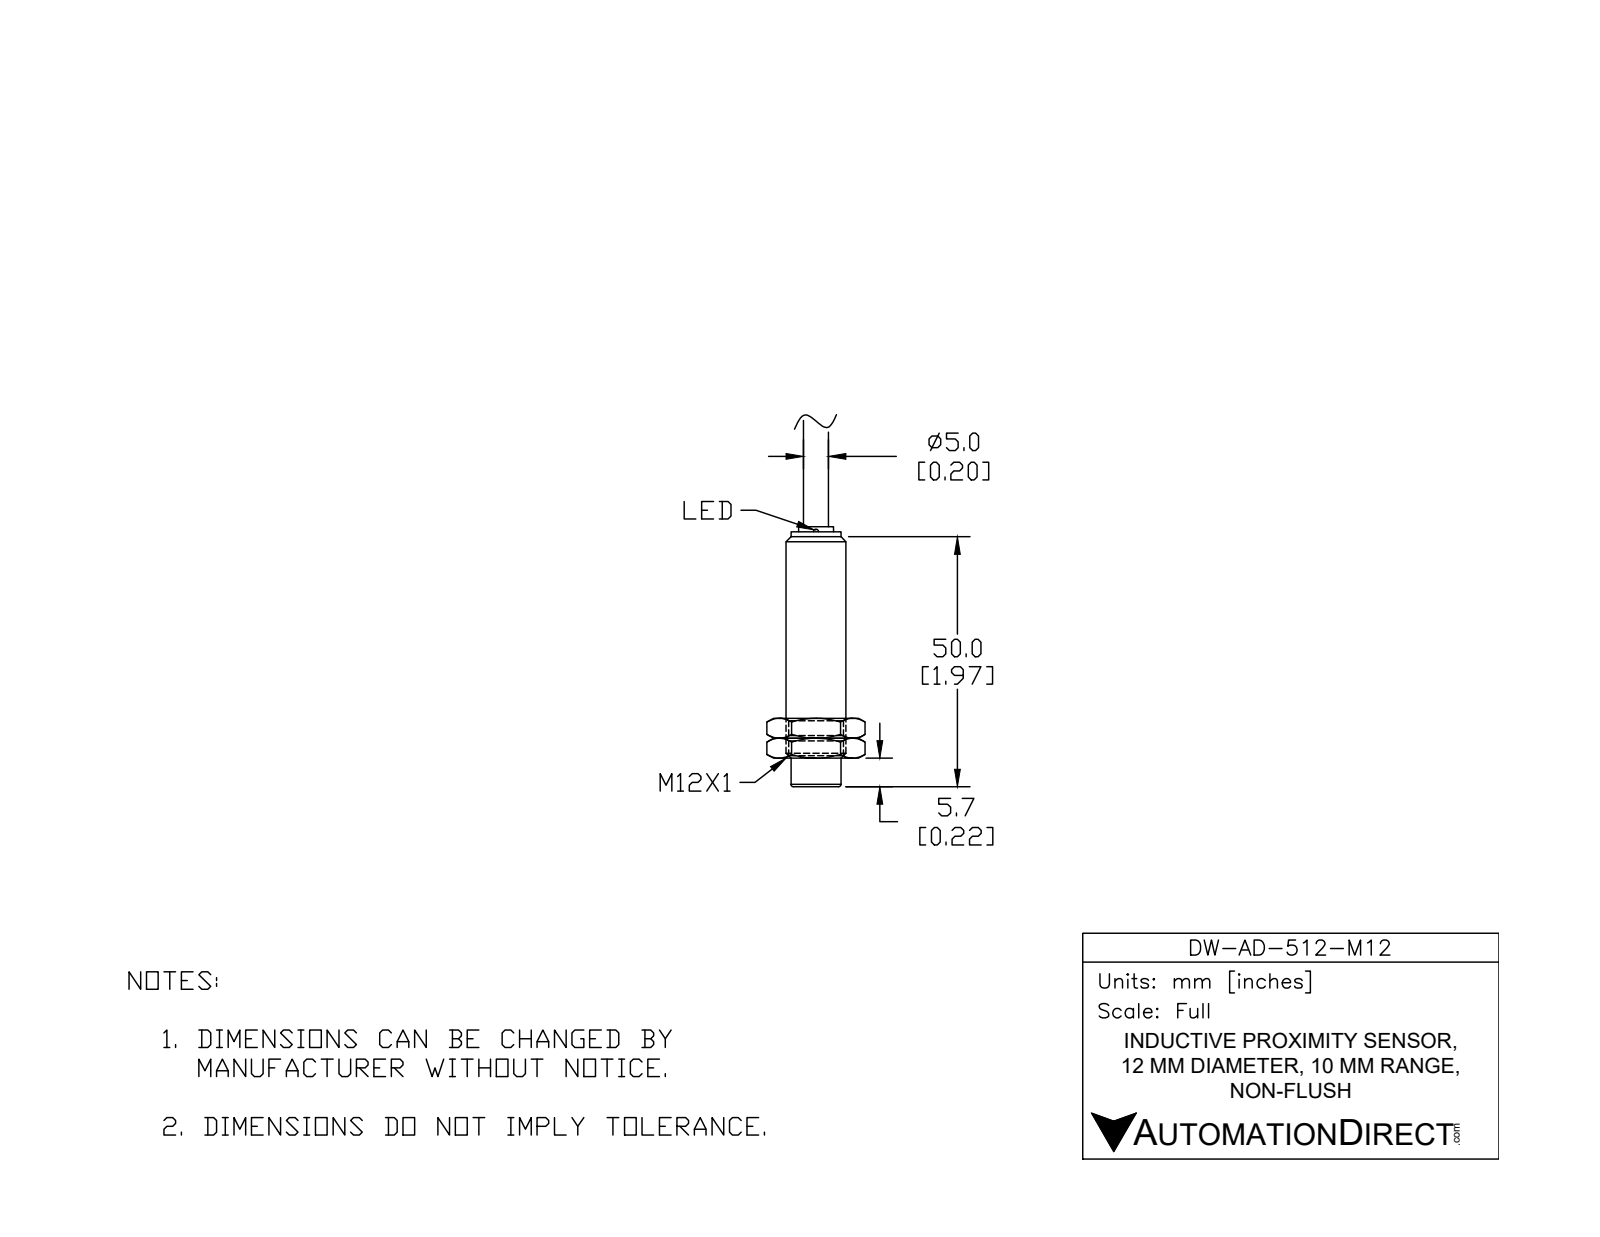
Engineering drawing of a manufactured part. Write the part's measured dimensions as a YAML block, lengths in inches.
part_name: "DW-AD-512-M12"
step_written_by: "SolidWorks 2017 (AUTOMOTIVE_DESIGN)"
units: inches
bodies: {solids: 1, faces: 30, planar: 15, cylindrical: 5, other: 10}
overall_size: [2.976, 0.472, 0.472]
volume: 0.369
surface_area: 3.799
round_bosses_or_shafts:
  - {diameter: 0.472, count: 1}
  - {diameter: 0.421, count: 1}
  - {diameter: 0.413, count: 1}
  - {diameter: 0.268, count: 1}
  - {diameter: 0.197, count: 1}
face_to_face_distances: [2, 2.047, 0.047, 2.031, 0.031, 0.016]
